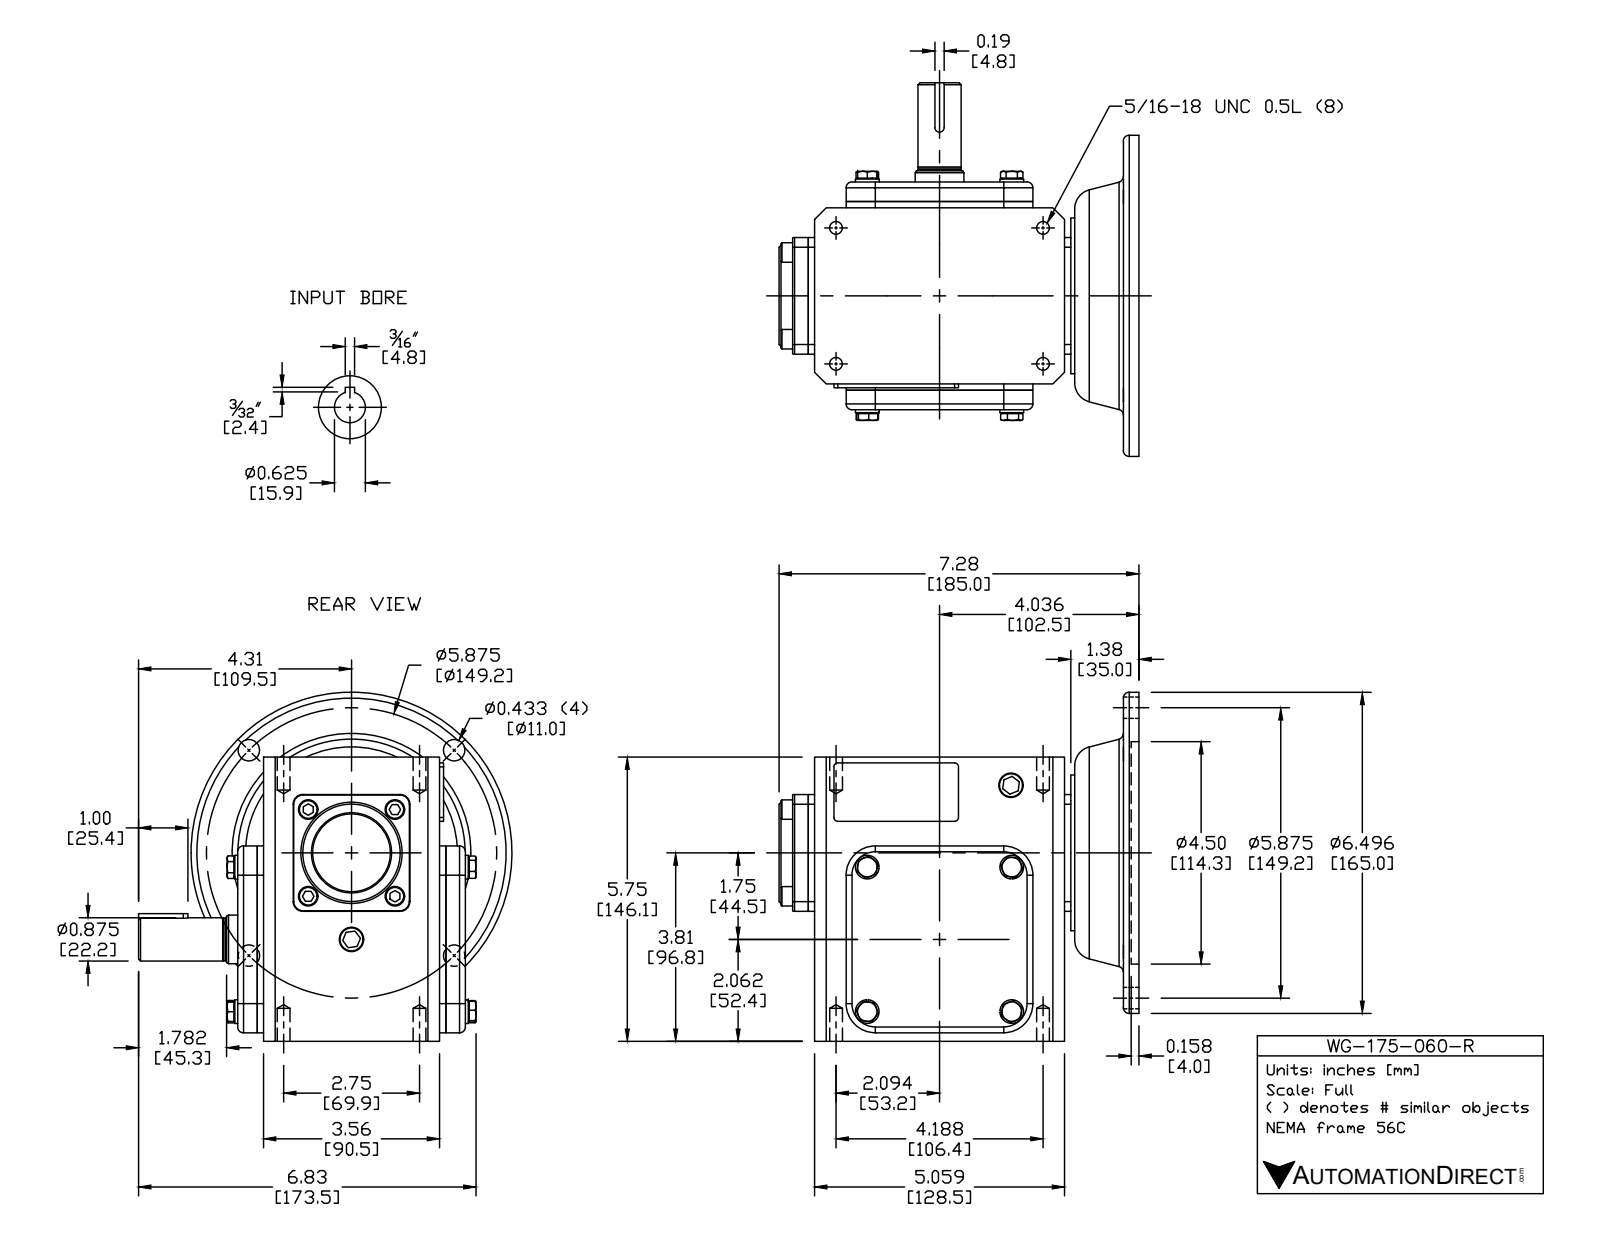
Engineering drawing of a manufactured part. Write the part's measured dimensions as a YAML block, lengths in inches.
part_name: "WG-175-060-R"
step_written_by: "SolidWorks 2015 (CONFIG_CONTROL_DESIGN)"
units: inches
bodies: {solids: 43, faces: 613, planar: 312, cylindrical: 172, other: 129}
overall_size: [7.559, 7.283, 7.06]
volume: 131.9
surface_area: 366.4
round_holes:
  - {diameter: 0.257, count: 4}
  - {diameter: 0.406, count: 4}
  - {diameter: 0.512, count: 1}
  - {diameter: 0.625, count: 1}
  - {diameter: 0.984, count: 1}
  - {diameter: 1.181, count: 1}
  - {diameter: 1.457, count: 1}
  - {diameter: 1.575, count: 1}
  - {diameter: 3.543, count: 1}
  - {diameter: 4.5, count: 1}
round_bosses_or_shafts:
  - {diameter: 0.394, count: 8}
  - {diameter: 0.48, count: 4}
  - {diameter: 0.512, count: 2}
  - {diameter: 6.496, count: 1}
  - {diameter: 3.15, count: 1}
  - {diameter: 2.047, count: 1}
  - {diameter: 1.575, count: 1}
  - {diameter: 0.875, count: 1}
partial_cylinders:
  - {radius: 0.079, count: 8}
  - {radius: 0.118, count: 8}
  - {radius: 0.197, count: 4}
  - {radius: 0.591, count: 4}
  - {radius: 0.02, count: 2}
  - {radius: 0.039, count: 2}
  - {radius: 0.094, count: 1}
face_to_face_distances: [0.128, 3.819, 4.213, 0.394, 4.085, 3.691, 0.522, 0.315, 5.75, 6.693]
hole_center_spacings: [2.937, 4.154, 2.103, 2.75, 4.188, 4.354, 5.01, 5.875]
